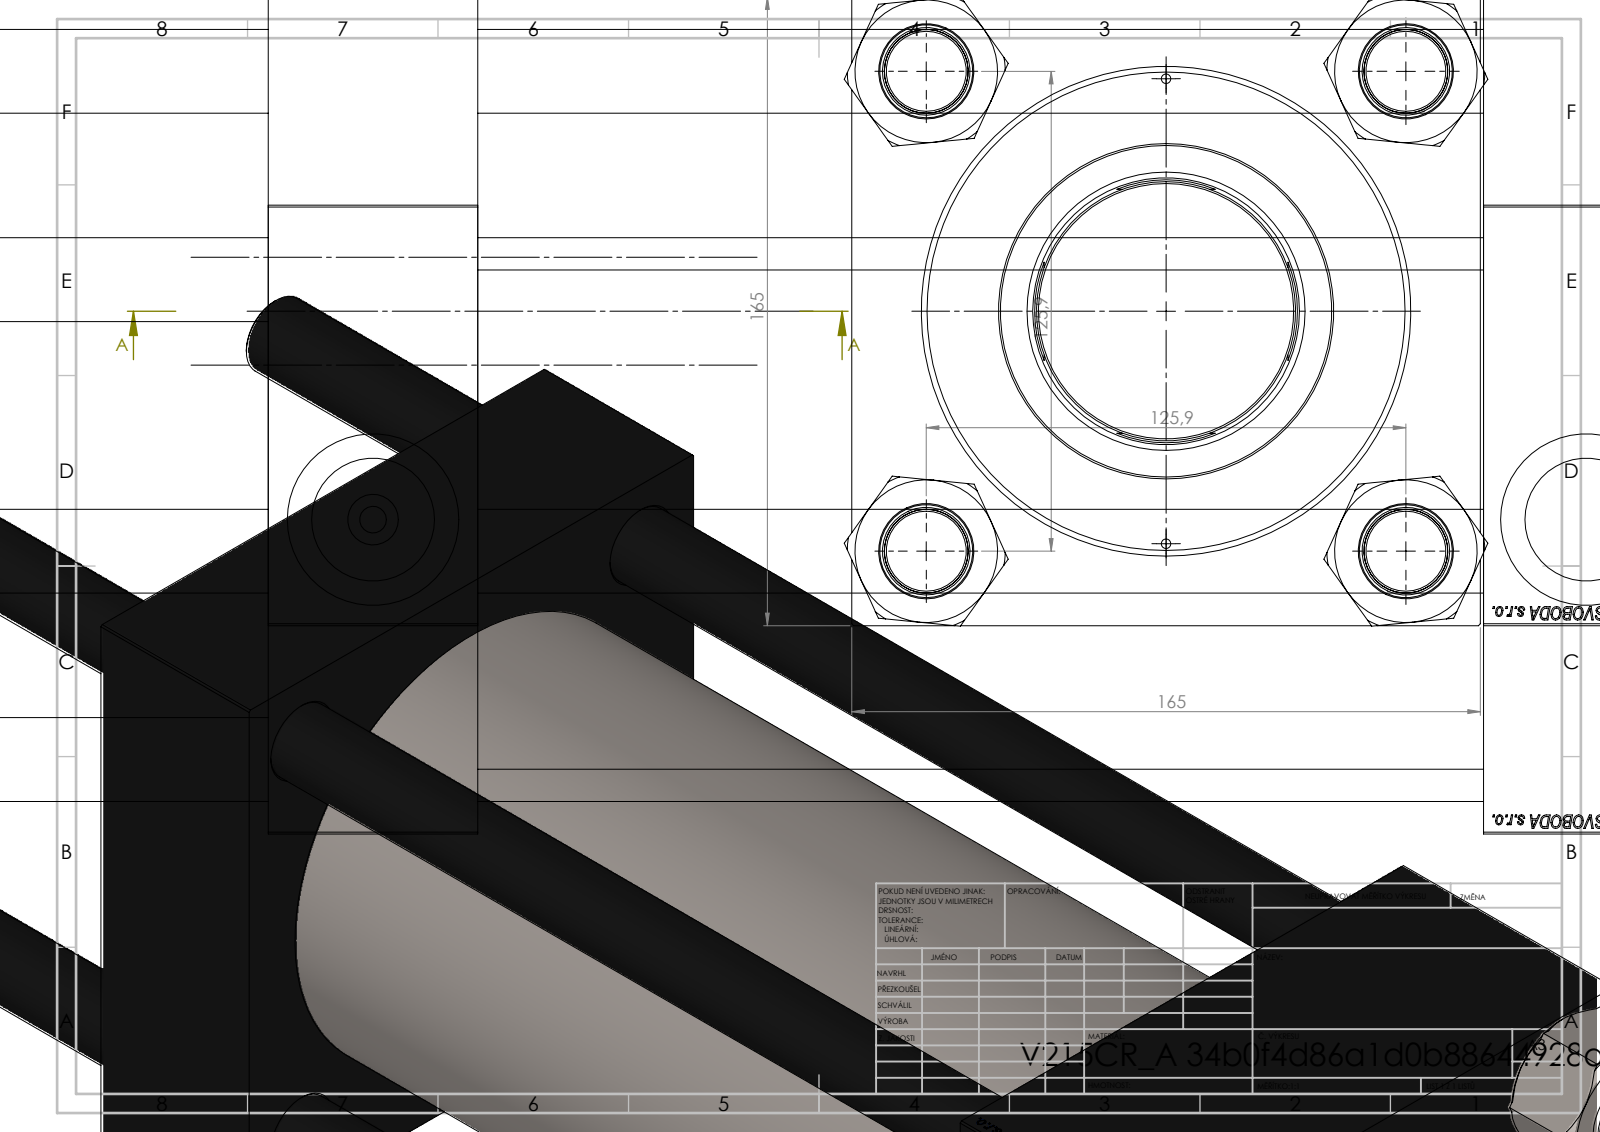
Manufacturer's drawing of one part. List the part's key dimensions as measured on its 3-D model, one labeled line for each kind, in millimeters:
Part name (STEP PRODUCT): V215CR_BODY_A; V215CR_ROD_END_F; V215CR_VCP; CR025_012_A_0_G_A_G_M_020_+#_##_TYCINKA (+2 more)
STEP written by: SolidWorks 2019 (CONFIG_CONTROL_DESIGN)
Units: millimetres
Bodies: 12 solids, 1202 faces (574 planar, 88 cylindrical, 540 other)
Overall size (bounding box): 581 × 168.94 × 165.27
Volume: 6 163 000 mm³ · Surface area: 810 057 mm²
Round holes (diameter × count): ⌀22 ×4, ⌀2.5 ×2, ⌀7 ×2, ⌀32.24 ×2, ⌀45 ×2, ⌀46.5 ×1, ⌀70 ×1, ⌀73 ×1, ⌀96 ×1, ⌀125 ×1, ⌀125.5 ×1
Round bosses / shafts (diameter × count): ⌀25 ×4, ⌀131 ×1, ⌀88 ×1, ⌀68 ×1, ⌀50 ×1, ⌀49 ×1
Main face-to-face distances: 165, 55, 397, 342, 319, 264, 78, 368.3, 313.3, 49.3
Hole centre spacings: 62.98, 89.02, 125.9, 139.02, 61, 178.05, 122, 318.5
